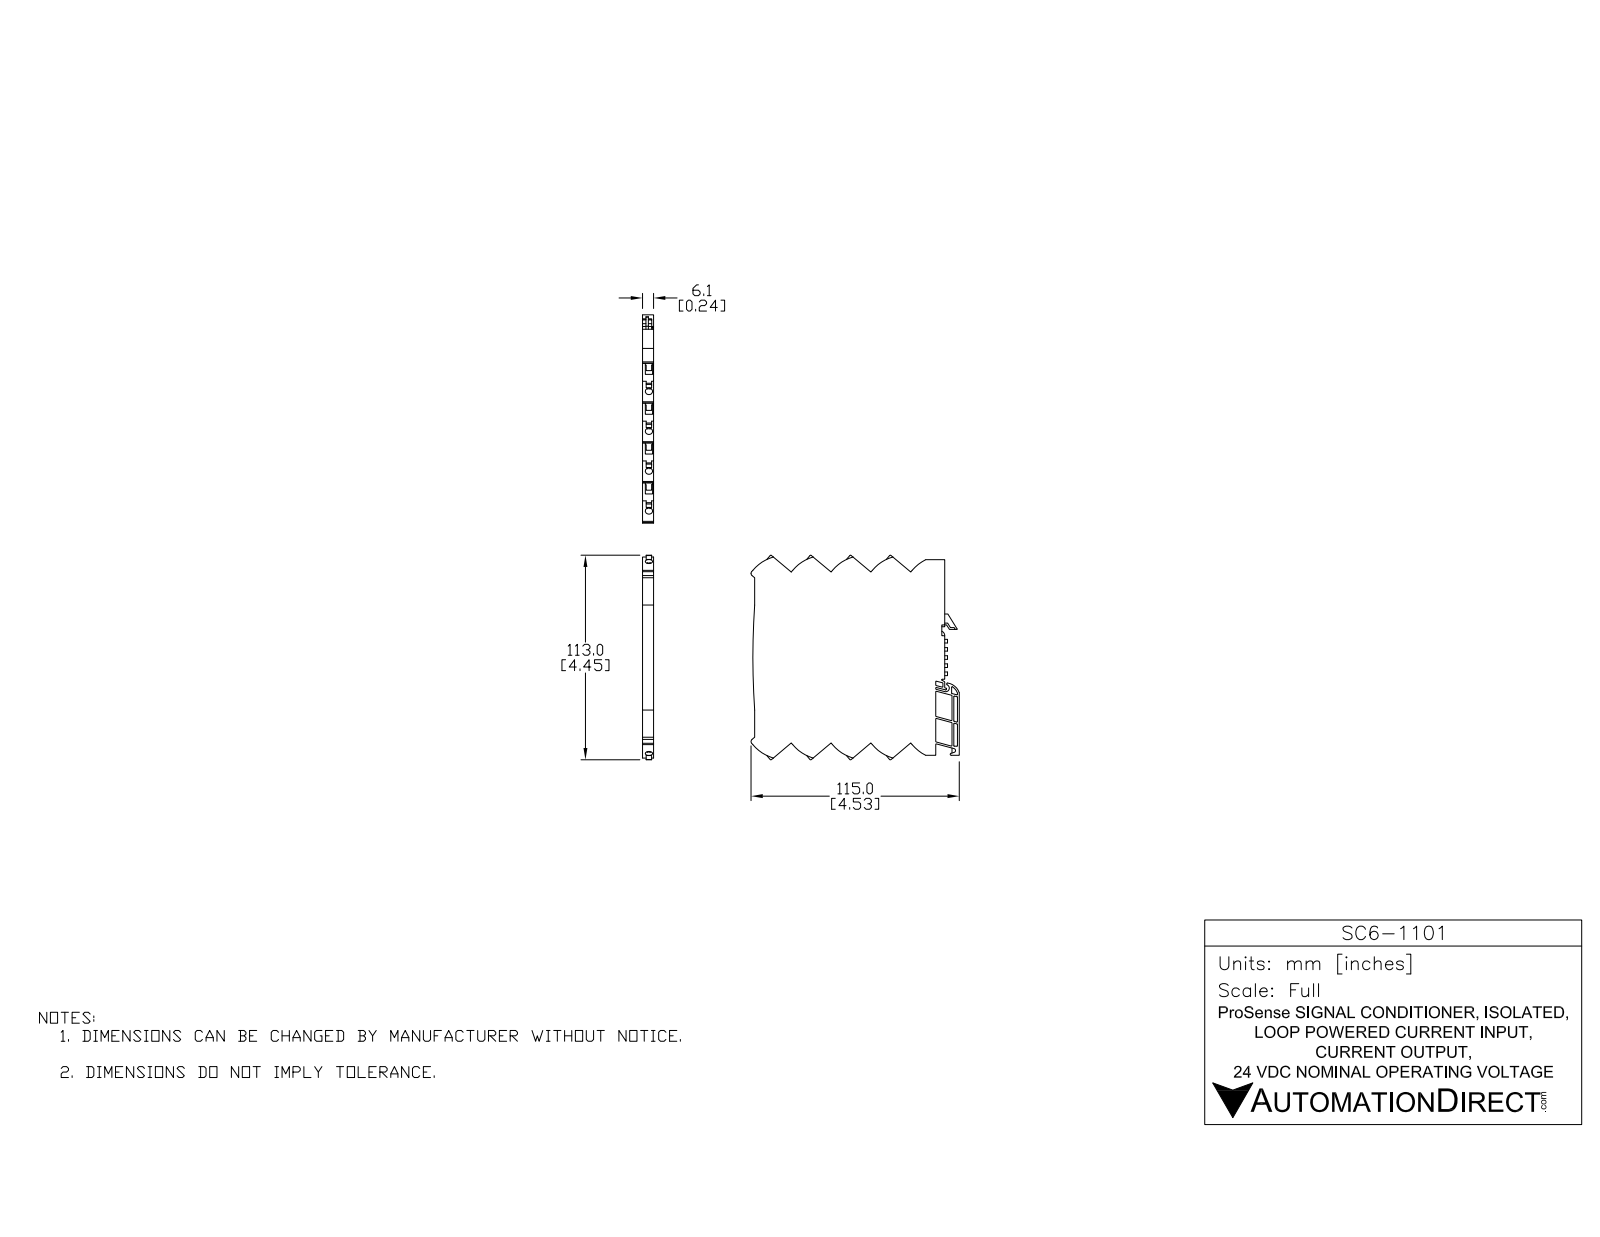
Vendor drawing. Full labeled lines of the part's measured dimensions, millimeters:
Part name (STEP PRODUCT): SC6-1101
STEP written by: SolidWorks 2017 (AUTOMOTIVE_DESIGN)
Units: millimetres
Bodies: 1 solid, 435 faces (328 planar, 107 cylindrical, 0 other)
Overall size (bounding box): 115 × 112.99 × 6.1
Volume: 65 156 mm³ · Surface area: 28 033 mm²
Round holes (diameter × count): ⌀4 ×8
Partial cylindrical surfaces — rounded edges, fillets, slot ends (radius × count): R0.3 ×33, R0.5 ×10, R1.5 ×10, R23.31 ×10, R0.2 ×2, R0.57 ×1, R1.08 ×1, R2 ×1
Main face-to-face distances: 6.1, 1, 3, 4, 2.05, 14.14, 4.05, 1.05, 3.5, 5.05
Hole centre spacings: 14.14, 28.28, 14.15, 42.42
